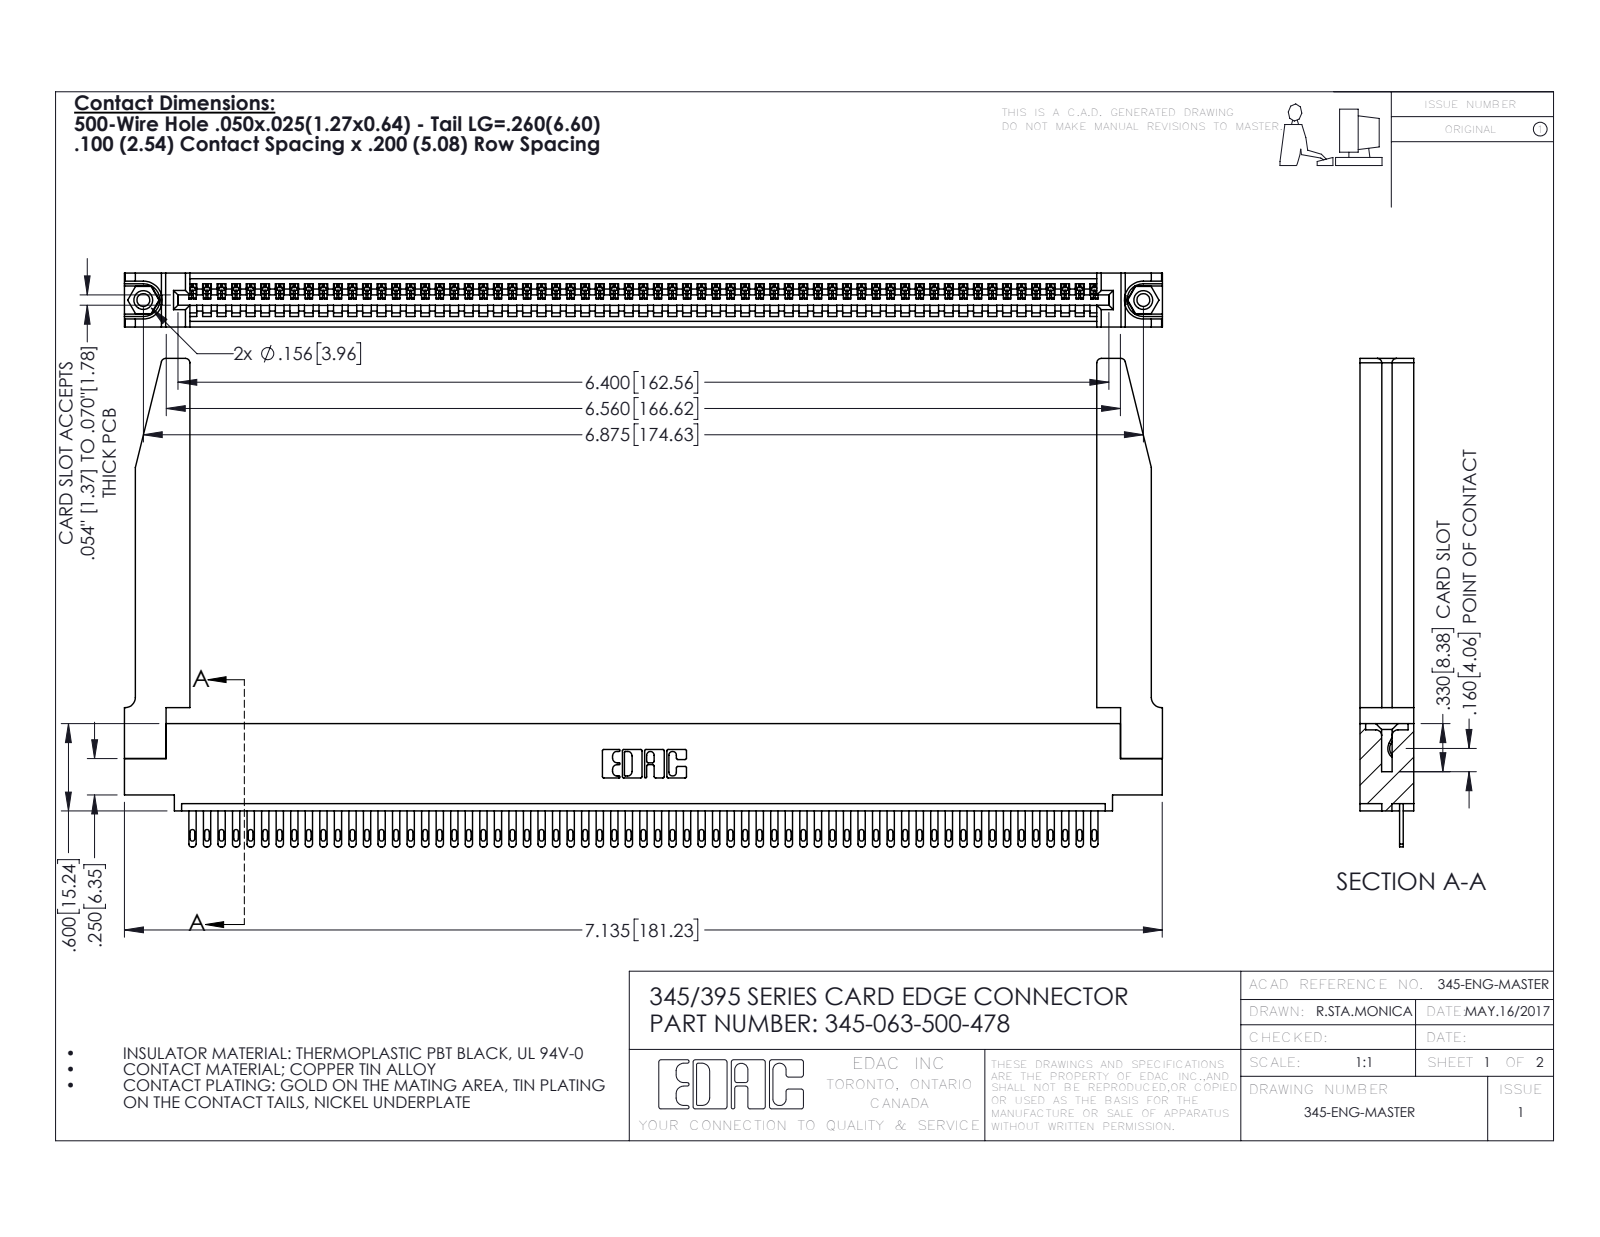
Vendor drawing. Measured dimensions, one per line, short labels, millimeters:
name: 345-063-500-478; 345-220-078_345-220-078; 345-292-001_345-293-100; 345-250-001_345-250-001-102 (+1 more)
written by: SolidWorks 2016 (CONFIG_CONTROL_DESIGN)
unit: mm
bodies: 68 solids, 3766 faces (2368 planar, 1346 cylindrical, 52 other)
size: 181.3 × 85.3 × 9.4
volume: 25 120 mm³; area: 30 410 mm²
holes: 2× ⌀2.3, 2× ⌀3.2, 2× ⌀4, 1× ⌀1.6
bosses: 2× ⌀3.9
rounds: 126× R0.2, 126× R0.4, 126× R0.5, 22× R0.3, 8× R0.8, 6× R0.2, 6× R0.8, 3× R0.7
face distances: 1.8, 7.6, 9.4, 2.5, 6.9, 0.6, 5.1, 5.7, 3.8, 3.8
hole spacings: 6.9, 168.6, 174.6
